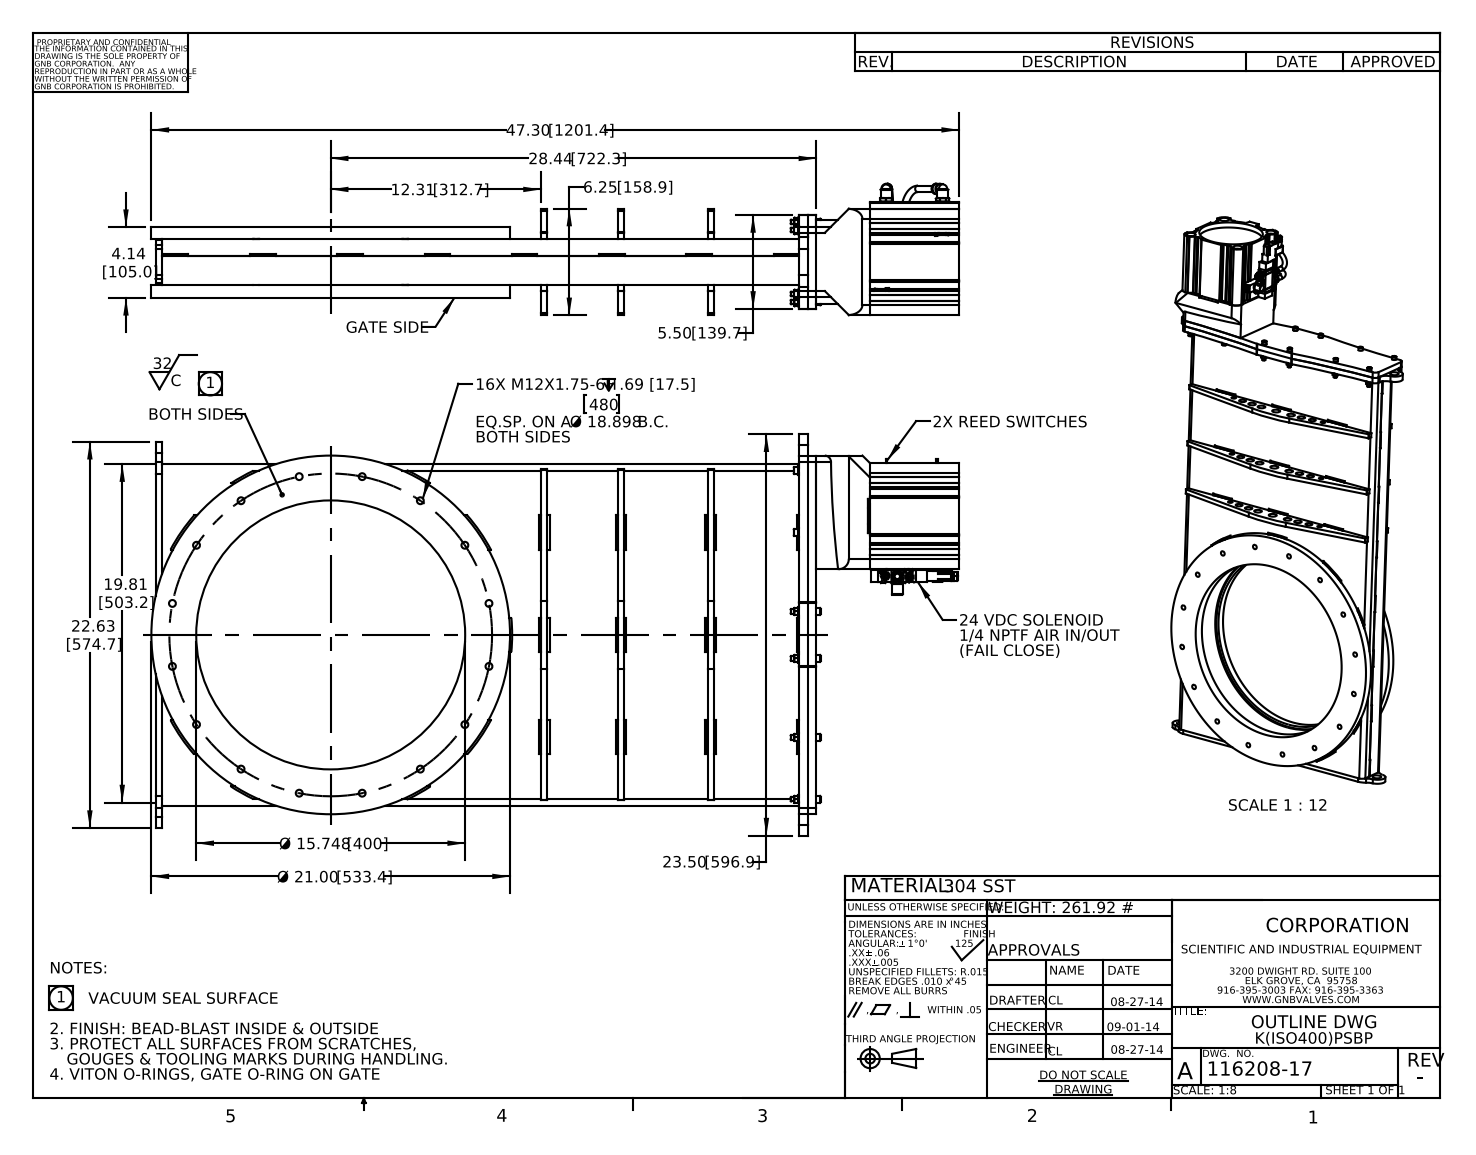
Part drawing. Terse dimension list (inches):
name: 116208-17
written by: SolidWorks 2015 (CONFIG_CONTROL_DESIGN)
unit: in
bodies: 0 solids, 1304 faces (600 planar, 507 cylindrical, 197 other)
size: 47.299 × 23.5 × 7.709
holes: 16× ⌀0.402, 4× ⌀0.4, 4× ⌀0.6, 4× ⌀0.65, 4× ⌀0.67, 4× ⌀0.77, 4× ⌀0.835, 3× ⌀0.131, 2× ⌀0.165, 2× ⌀0.7, 1× ⌀0.315, 1× ⌀5.591
bosses: 16× ⌀0.375, 12× ⌀0.487, 8× ⌀0.25, 4× ⌀0.439, 2× ⌀0.709, 2× ⌀0.669, 2× ⌀0.606, 2× ⌀0.555
rounds: 32× R0.039, 12× R0.375, 9× R0.02, 8× R0.08, 8× R0.75, 8× R1, 4× R0.031, 4× R0.2
face distances: 0.187, 2.507, 2.32, 2.695, 0.375, 0.687, 3.448, 3.26, 0.94, 0.753
hole spacings: 10.499, 17.459, 7.232, 15.713, 18.535, 3.687, 13.363, 9.449
